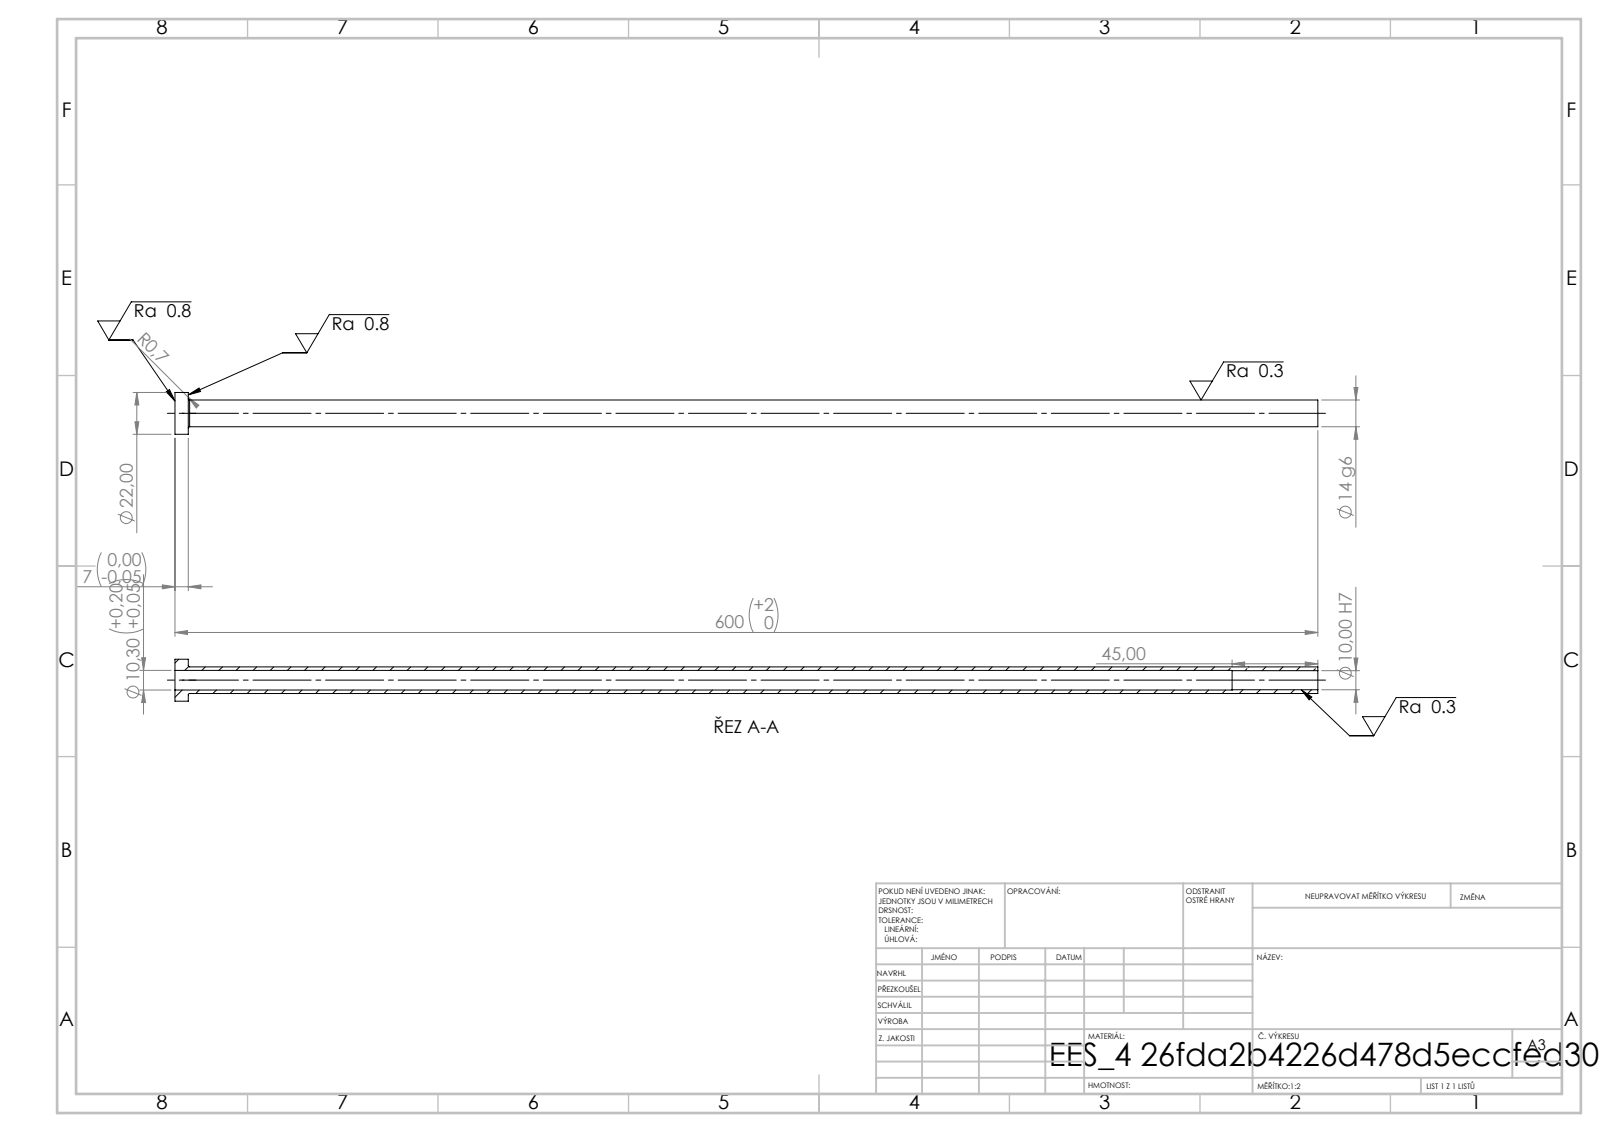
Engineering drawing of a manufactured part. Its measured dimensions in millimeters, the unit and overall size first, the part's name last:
Units: millimetres
Overall size (bounding box): 600 × 22 × 22
Round holes (diameter × count): ⌀10 ×1, ⌀10.3 ×1
Round bosses / shafts (diameter × count): ⌀22 ×1, ⌀14 ×1
Main face-to-face distances: 7, 600, 593, 555, 548, 45
Volume: 44 172 mm³ · Surface area: 46 528 mm²
Bodies: 1 solid, 14 faces (4 planar, 8 cylindrical, 2 other)
STEP written by: SolidWorks 2019 (CONFIG_CONTROL_DESIGN)
